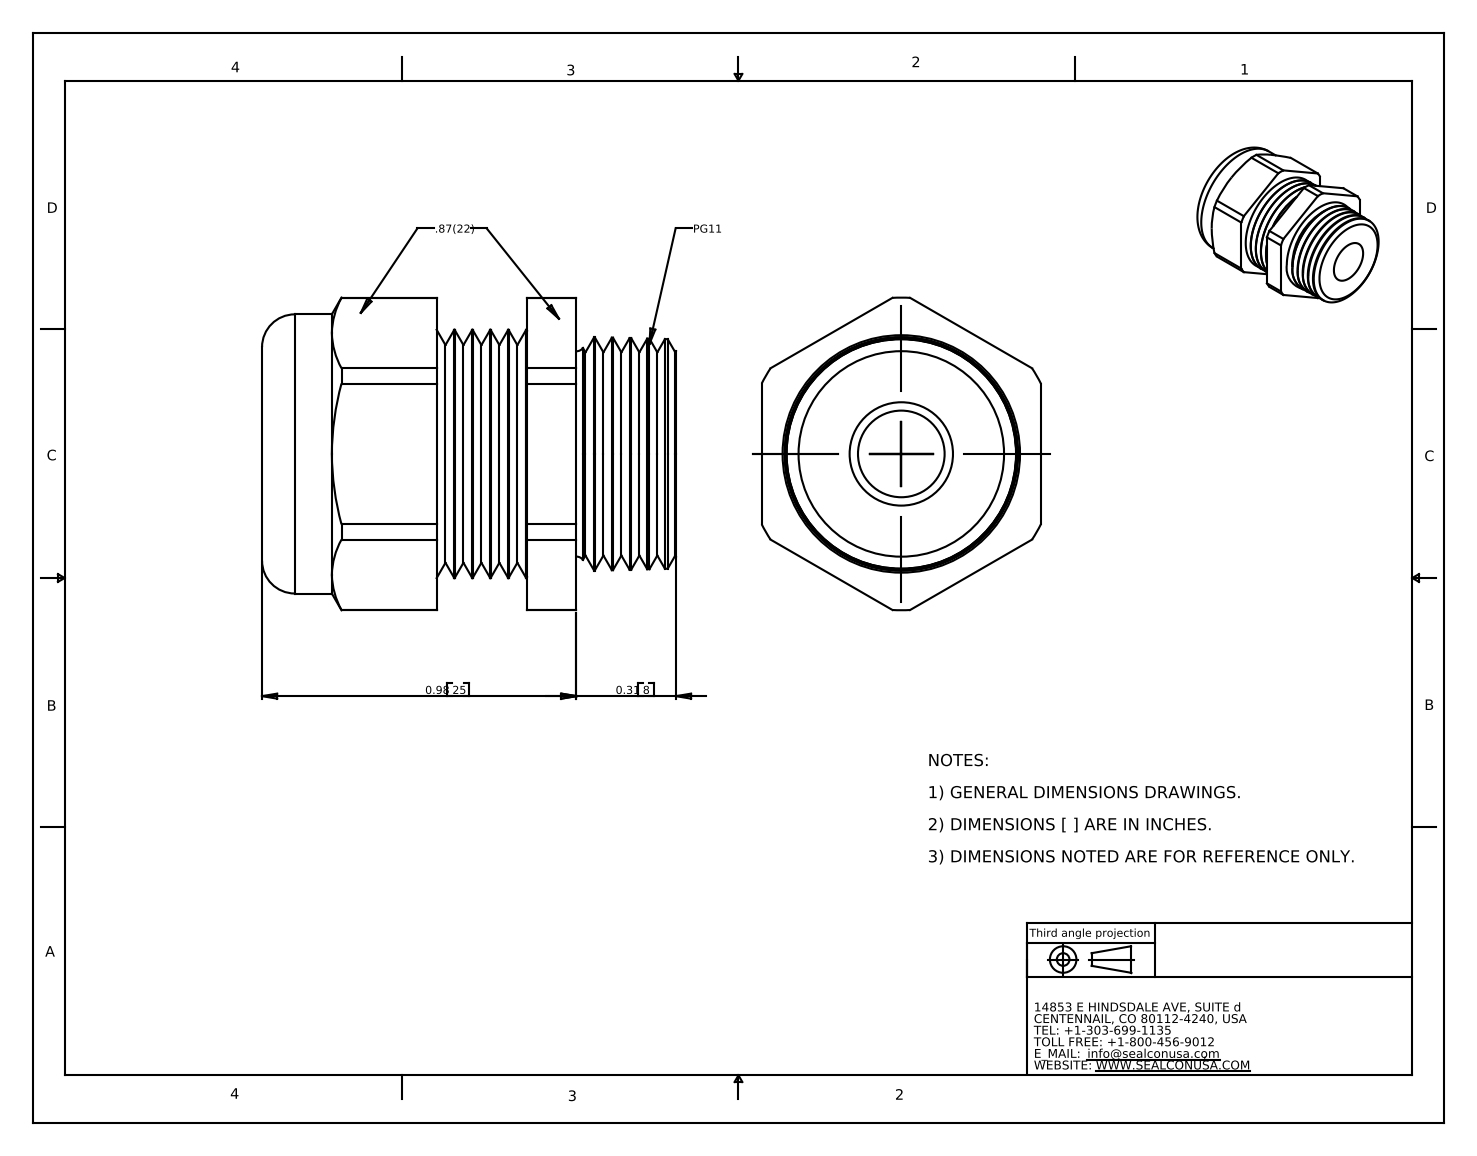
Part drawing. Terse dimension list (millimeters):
name: CD11AR-GY
written by: SolidWorks 2007 (CONFIG_CONTROL_DESIGN)
unit: mm
bodies: 2 solids, 128 faces (20 planar, 34 cylindrical, 74 other)
size: 32.8 × 24.7 × 22.1
volume: 9 390 mm³; area: 5 655 mm²
holes: 1× ⌀6.9, 1× ⌀15.7
bosses: 1× ⌀22.1, 1× ⌀19.7
rounds: 1× R12.4
face distances: 22.1, 27.2, 5, 32.3, 24.4, 19.4, 7.9, 13.3, 8.3, 11.1
